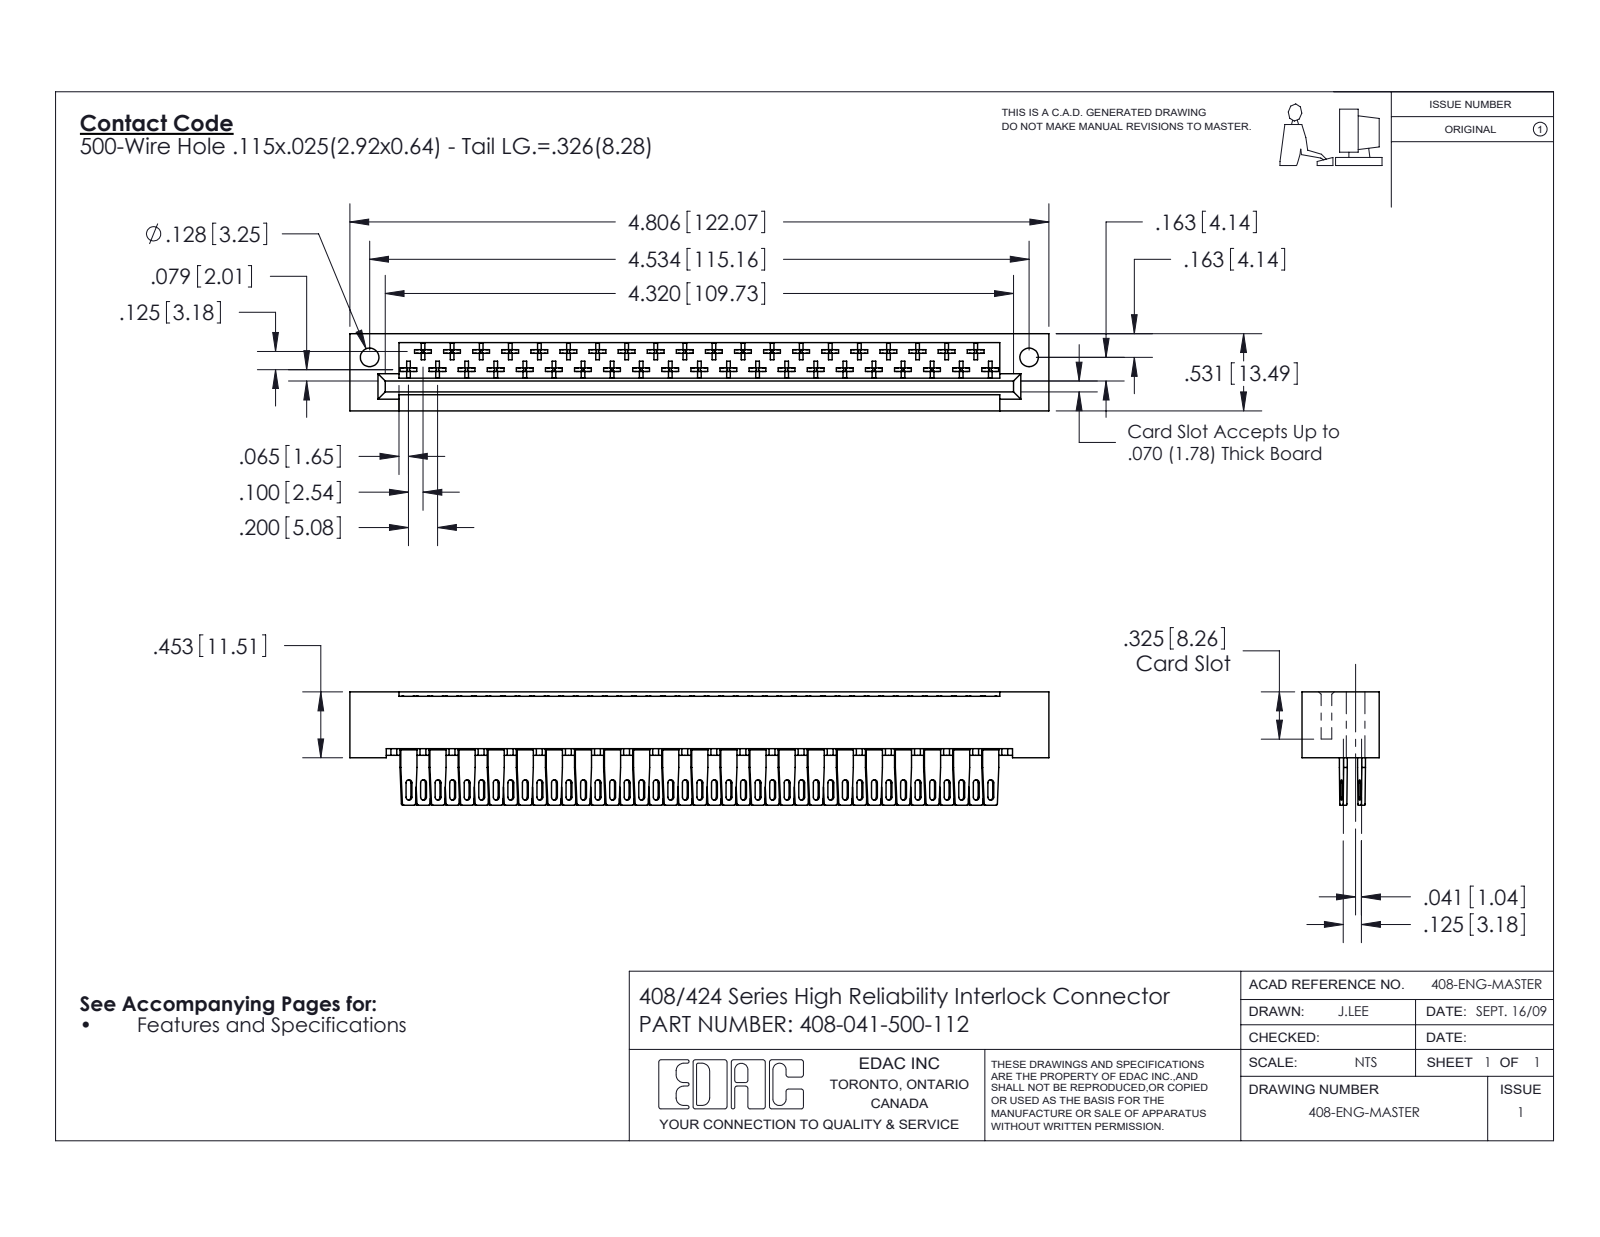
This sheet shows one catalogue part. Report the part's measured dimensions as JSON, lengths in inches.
{"part_name": "408 Part_041 - 1; 408-290-001_408-290-100; 408-047-500-112", "step_written_by": "SolidWorks 2016 (CONFIG_CONTROL_DESIGN)", "units": "inches", "bodies": {"solids": 42, "faces": 2381, "planar": 1717, "cylindrical": 500, "other": 164}, "overall_size": [4.806, 0.779, 0.531], "volume_in3": 0.874, "surface_area_in2": 28.31, "round_holes": [[0.128, 2]], "partial_cylinders_radius": [[0.01, 328], [0.021, 82], [0.02, 43]], "face_to_face_distances": [0.531, 0.1, 0.125, 0.025, 0.025, 0.4, 0.259, 0.272, 0.235, 0.296], "hole_center_spacings": [4.534]}
